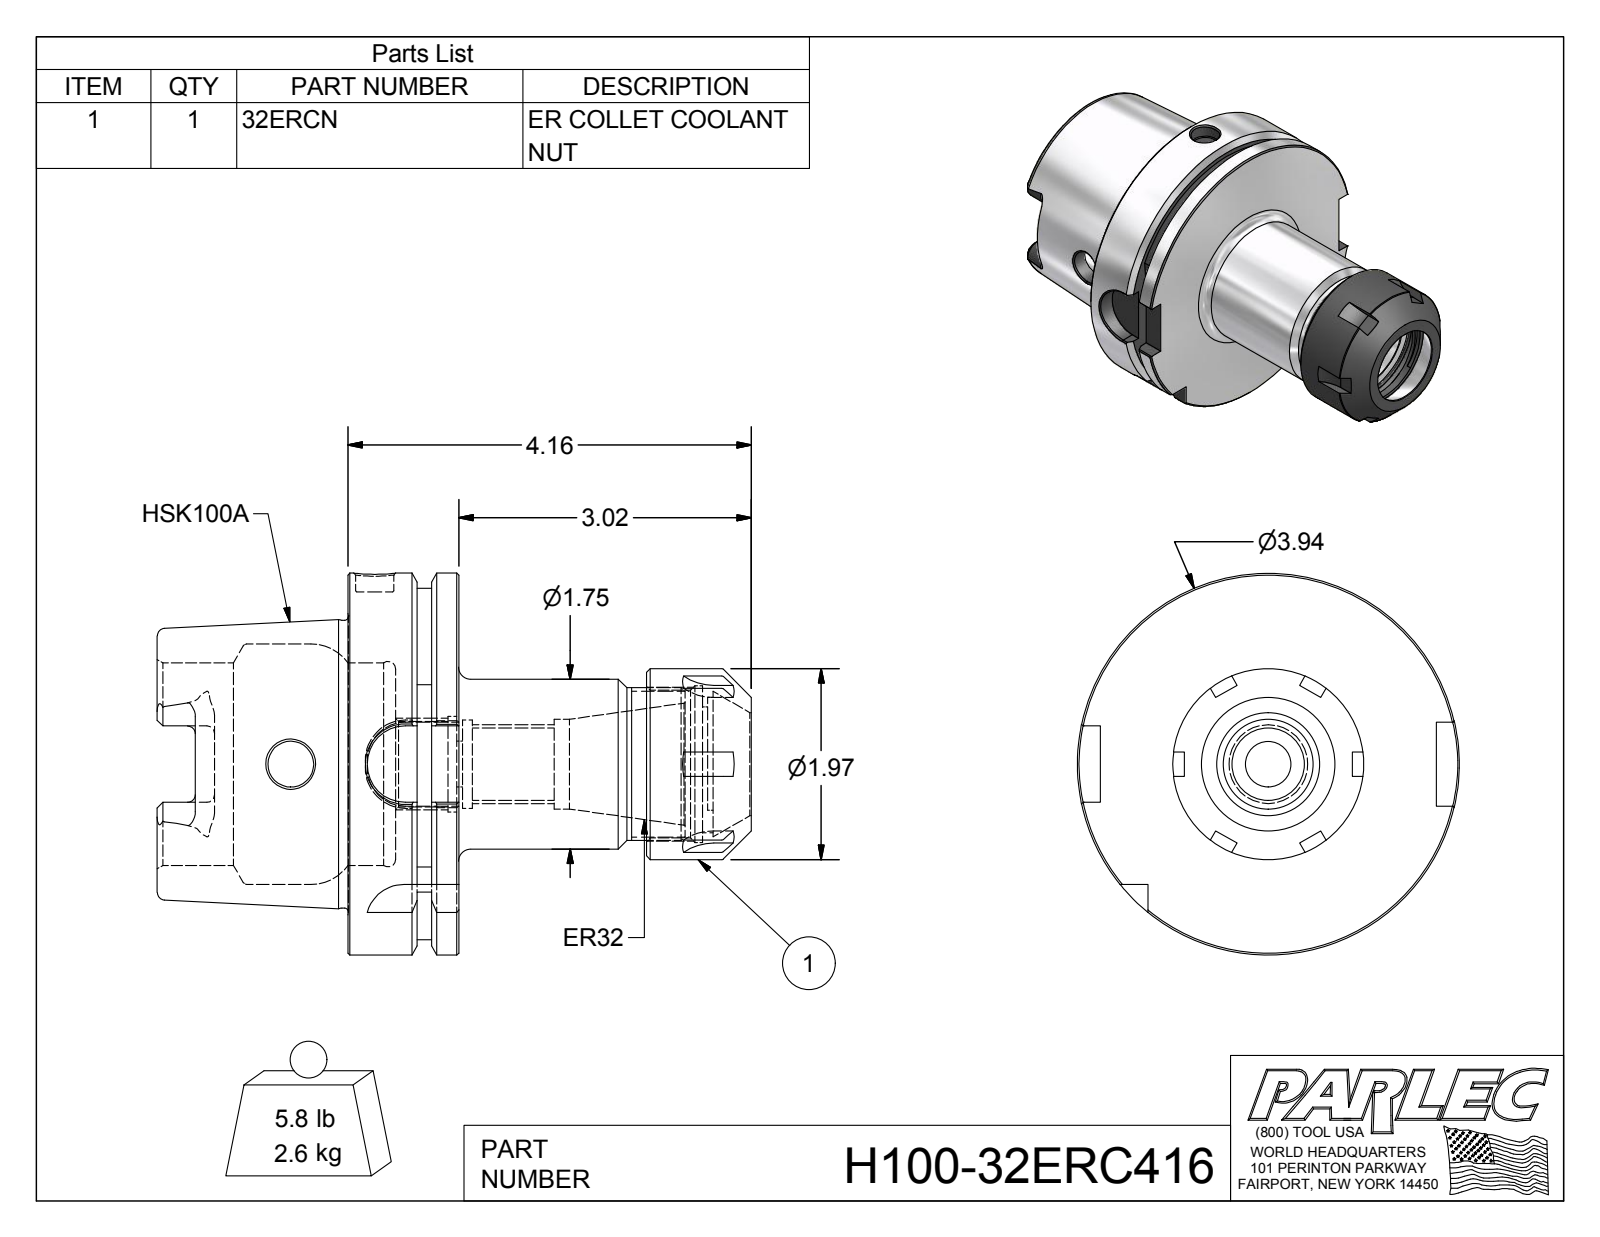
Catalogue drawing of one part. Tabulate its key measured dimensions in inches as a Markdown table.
| quantity | value |
| --- | --- |
| part name | H100-32ERC416; H100-32ER4-1; 32ERCN |
| STEP written by | Autodesk Inventor 2012 (AUTOMOTIVE_DESIGN) |
| units | inches |
| bodies | 2 solids, 176 faces (68 planar, 48 cylindrical, 60 other) |
| overall size | 6.129 × 3.937 × 3.937 |
| volume | 20.38 in³ |
| surface area | 111.2 in² |
| round holes (diameter × count) | 0.472 × 2, 0.394 × 1, 0.745 × 1, 0.881 × 1, 0.912 × 1, 0.925 × 1, 0.985 × 1, 1.063 × 1, 1.299 × 1, 1.522 × 1, 1.614 × 1, 2.087 × 1 |
| round bosses / shafts (diameter × count) | 3.937 × 1, 2.967 × 1, 1.969 × 1, 1.75 × 1, 1.575 × 1 |
| partial cylindrical surfaces (radius × count) | 0.079 × 6, 0.5 × 6, 0.192 × 4, 0.394 × 4, 0.689 × 1, 1.811 × 1 |
| main face-to-face distances | 1.142, 0.492, 0.65, 1.969, 2.461, 3.11, 2.83, 0.861, 0.369, 0.28 |
| hole center spacings | 0.059 |
